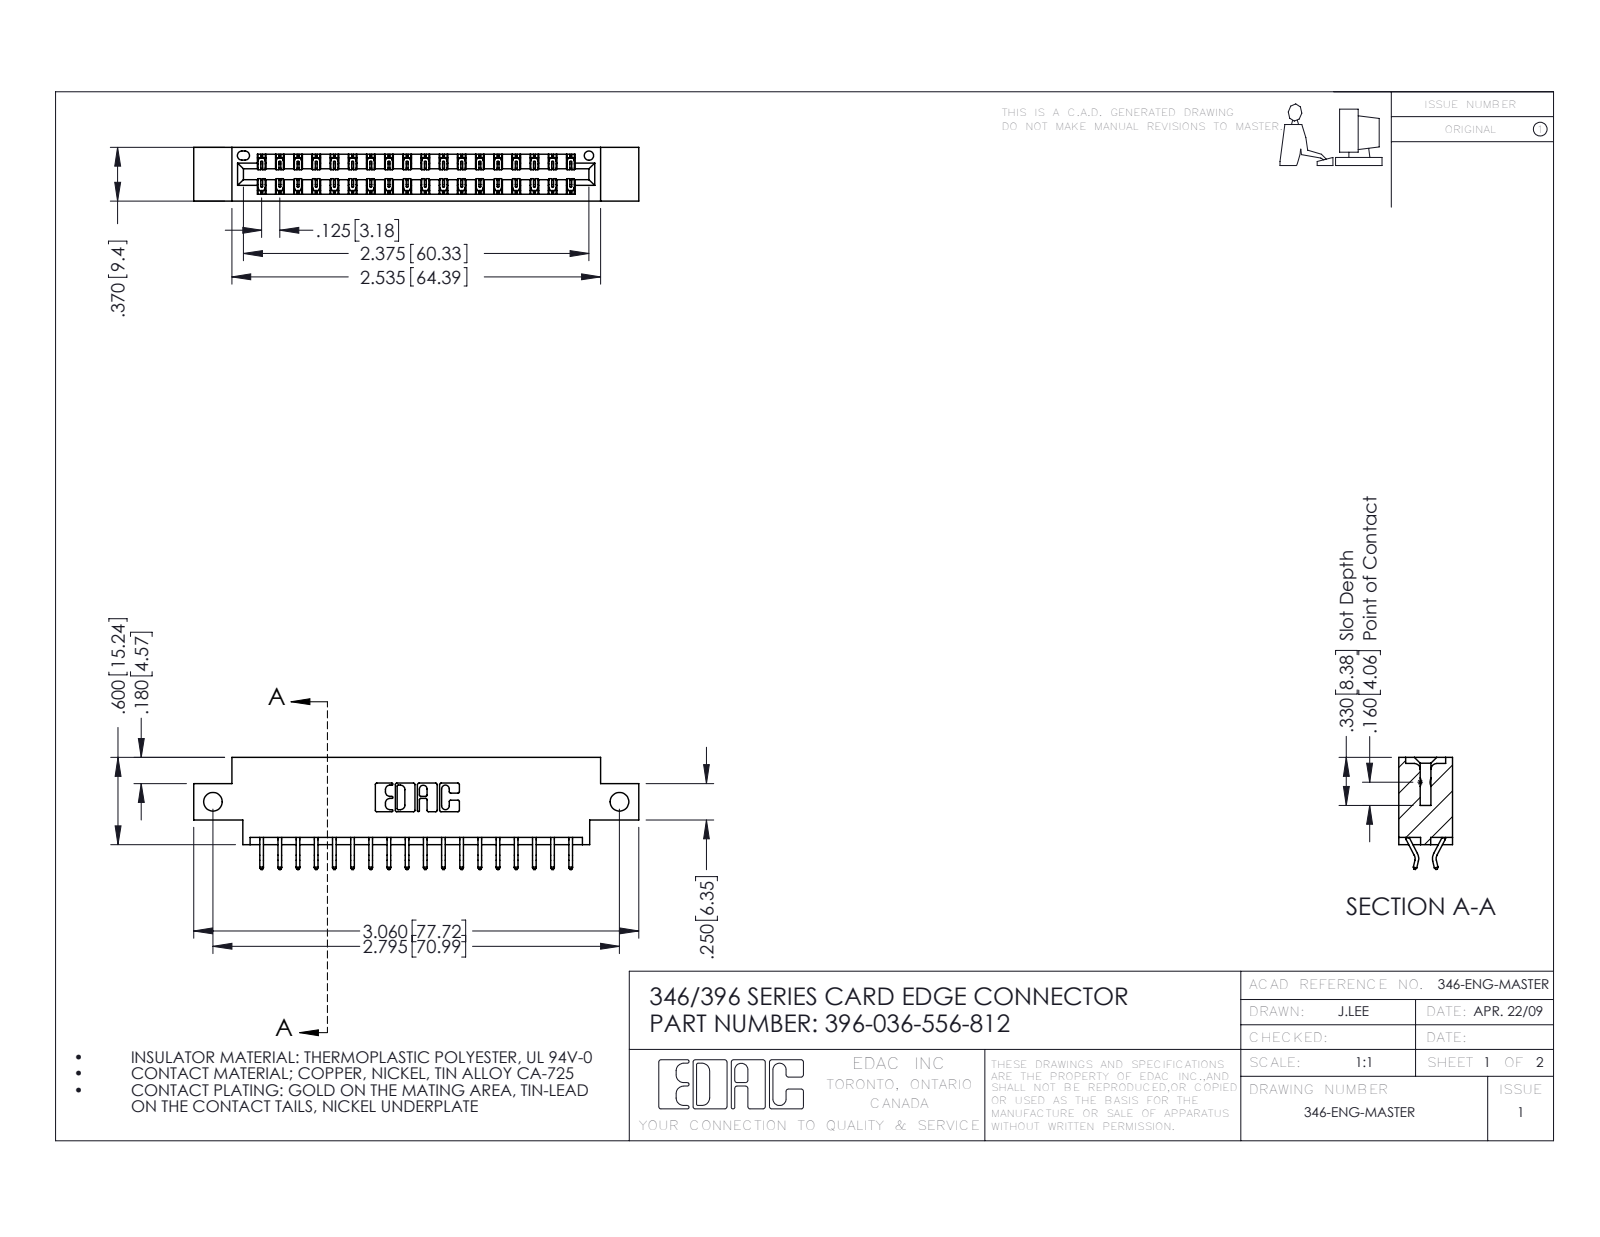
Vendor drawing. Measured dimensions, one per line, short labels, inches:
name: 345-292-001_556 Tail; 346 Part_0.170 Offset - Side Mount; 396-036-556-812
written by: SolidWorks 2016 (CONFIG_CONTROL_DESIGN)
unit: in
bodies: 37 solids, 2214 faces (1484 planar, 730 cylindrical, 0 other)
size: 3.06 × 0.77 × 0.37
volume: 0.436 in³; area: 14.66 in²
holes: 2× ⌀0.128, 1× ⌀0.064
rounds: 54× R0.006, 22× R0.01, 6× R0.007, 6× R0.031, 3× R0.026, 2× R0.01, 2× R0.014, 2× R0.022
face distances: 0.048, 0.322, 0.37, 0.25, 0.025, 0.072, 0.298, 0.275, 0.148, 0.222
hole spacings: 2.795
